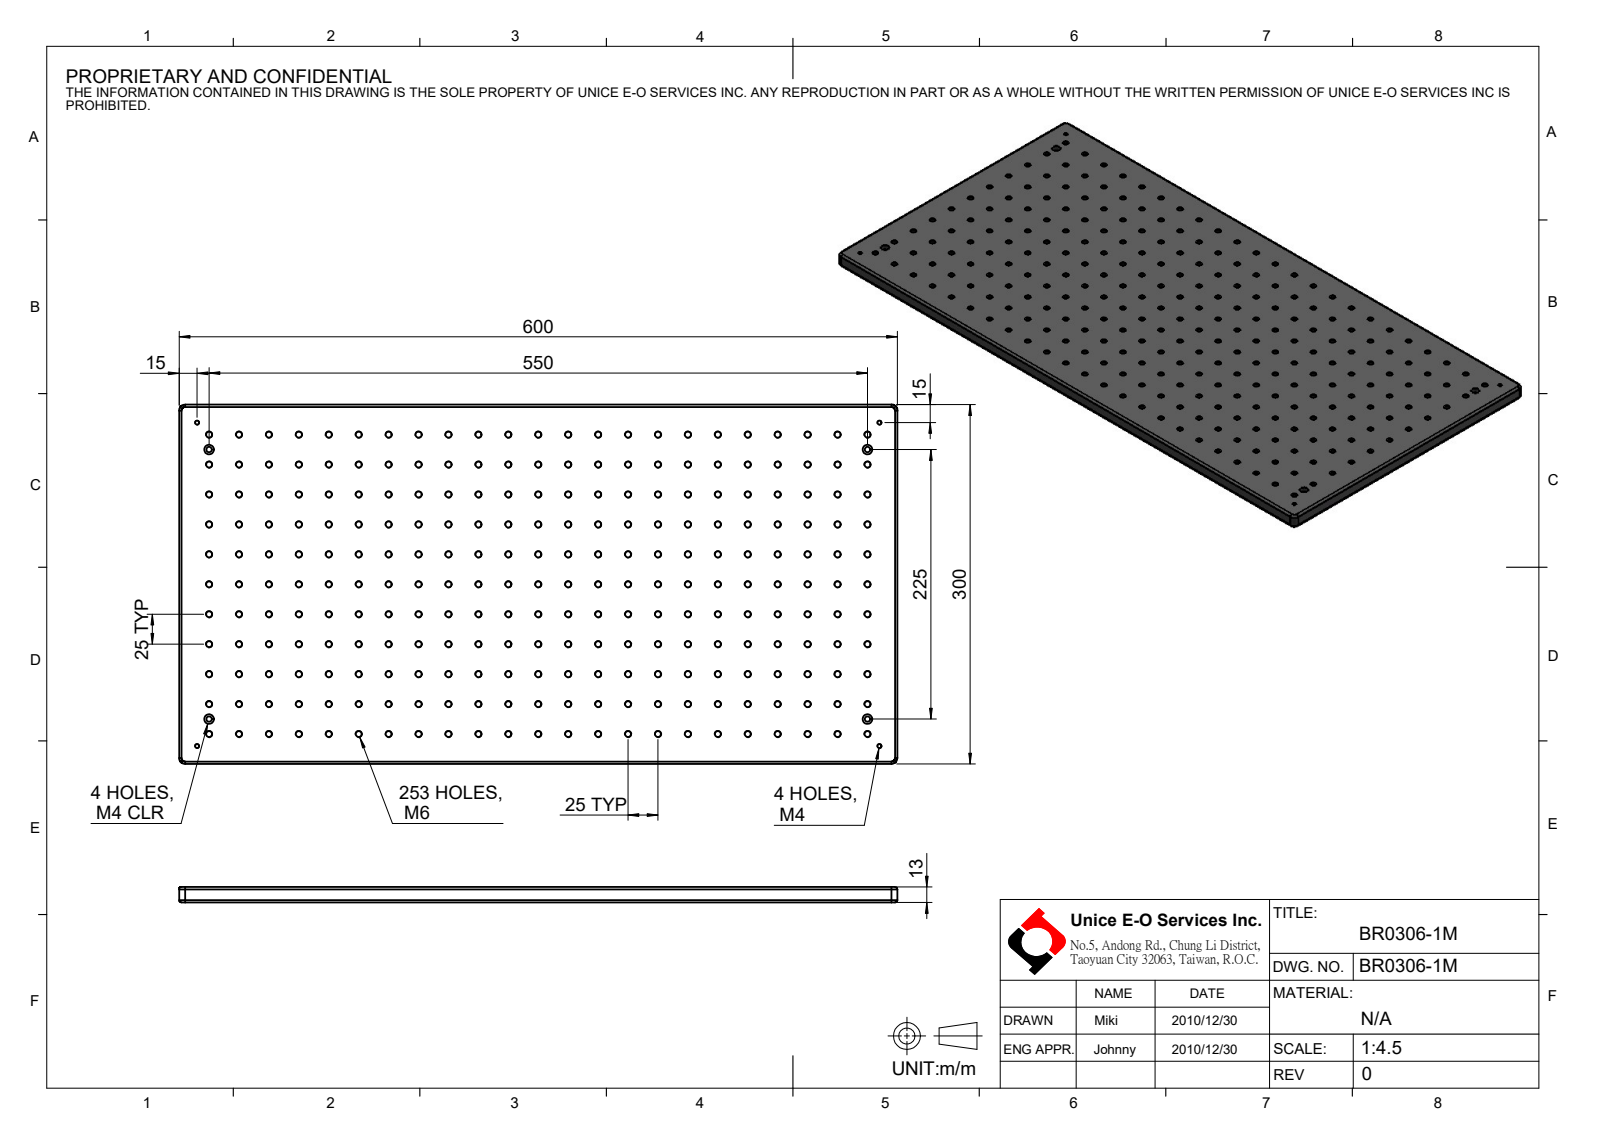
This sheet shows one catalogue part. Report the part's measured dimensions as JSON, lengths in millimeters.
{"part_name": "BR0306-1M", "step_written_by": "SolidWorks 2016 (CONFIG_CONTROL_DESIGN)", "units": "millimeters", "bodies": {"solids": 1, "faces": 560, "planar": 10, "cylindrical": 542, "other": 8}, "overall_size": [600, 300, 13], "volume_mm3": 2270000, "surface_area_mm2": 423167, "round_holes": [[5, 253], [3.3, 4], [4.5, 4], [8, 4]], "partial_cylinders_radius": [[2, 8], [5, 4]], "face_to_face_distances": [13, 300, 600, 8.6, 4.4], "hole_center_spacings": [25, 50, 75, 100, 125, 150, 175, 225]}
